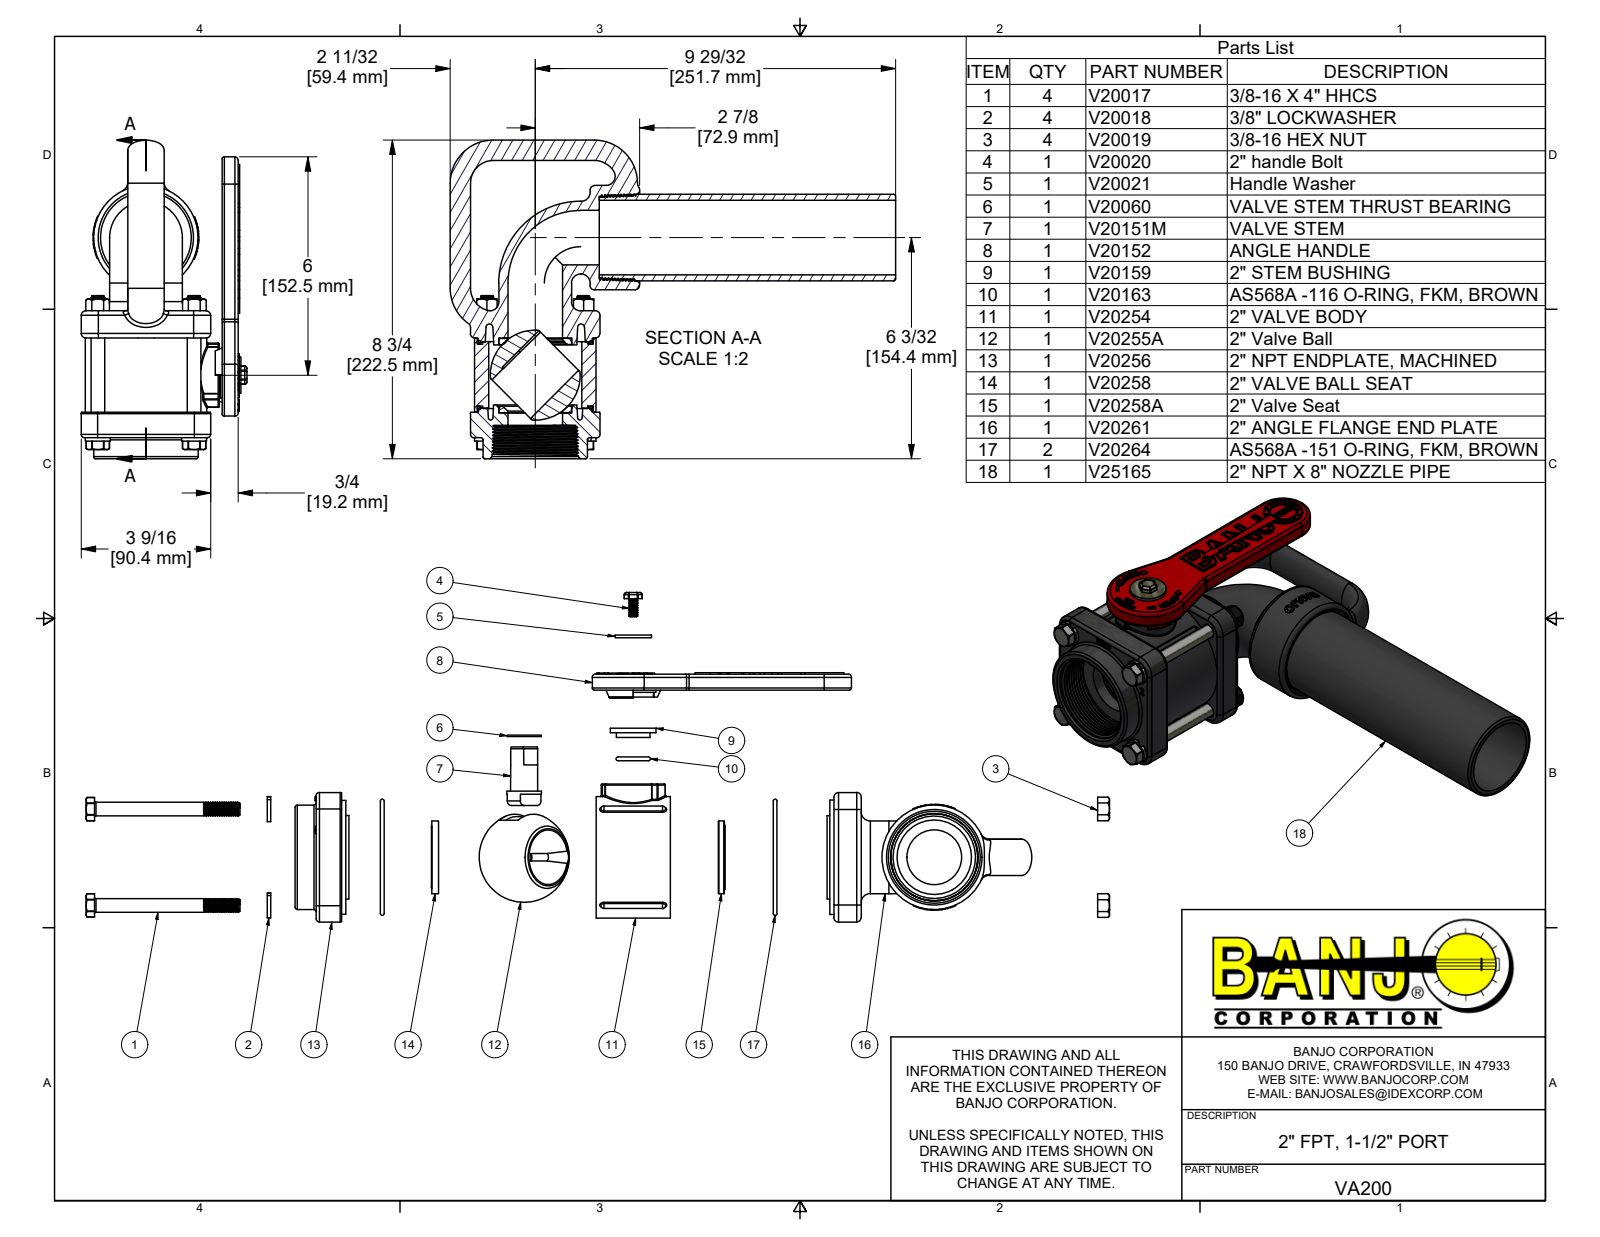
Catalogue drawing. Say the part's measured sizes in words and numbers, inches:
The part is named "VA200; V20254; V20256; VX20256 (+8 more)". Its 3-D file was written by "Autodesk Inventor 2013 (AUTOMOTIVE_DESIGN)". It is 27 solids with 2059 faces: 786 planar, 507 cylindrical and 766 other. Overall it measures 12.25 by 8.76 by 4.571 inches. Its volume is 46.75 cubic inches and its surface area 485.9 square inches. Round holes: 10 of diameter 0.165, 4 of diameter 0.307, 4 of diameter 0.375, 4 of diameter 0.385, 4 of diameter 0.406, 4 of diameter 0.407, 3 of diameter 1.5, 1 of diameter 0.196, 1 of diameter 0.281, 1 of diameter 0.726, 1 of diameter 0.75, 1 of diameter 0.751. Round bosses or shafts: 60 of diameter 0.324, 4 of diameter 0.687, 4 of diameter 0.5, 4 of diameter 0.375, 2 of diameter 2.87, 2 of diameter 2, 1 of diameter 3.34, 1 of diameter 3.145. Partial cylindrical surfaces (rounded edges, fillets, slot ends): 38 of radius 0.03, 22 of radius 0.09, 17 of radius 0.125, 12 of radius 0.06, 8 of radius 0.162, 4 of radius 0.015, 4 of radius 0.094, 4 of radius 0.32. The main face-to-face distances are 2.79, 0.75, 0.115, 3.56, 0.245, 2.04, 1.925, 0.42, 0.02, 0.7. The hole center spacings are 1.363, 2.316, 2.322, 2.632, 2.654, 0.705, 0.971, 0.977.
